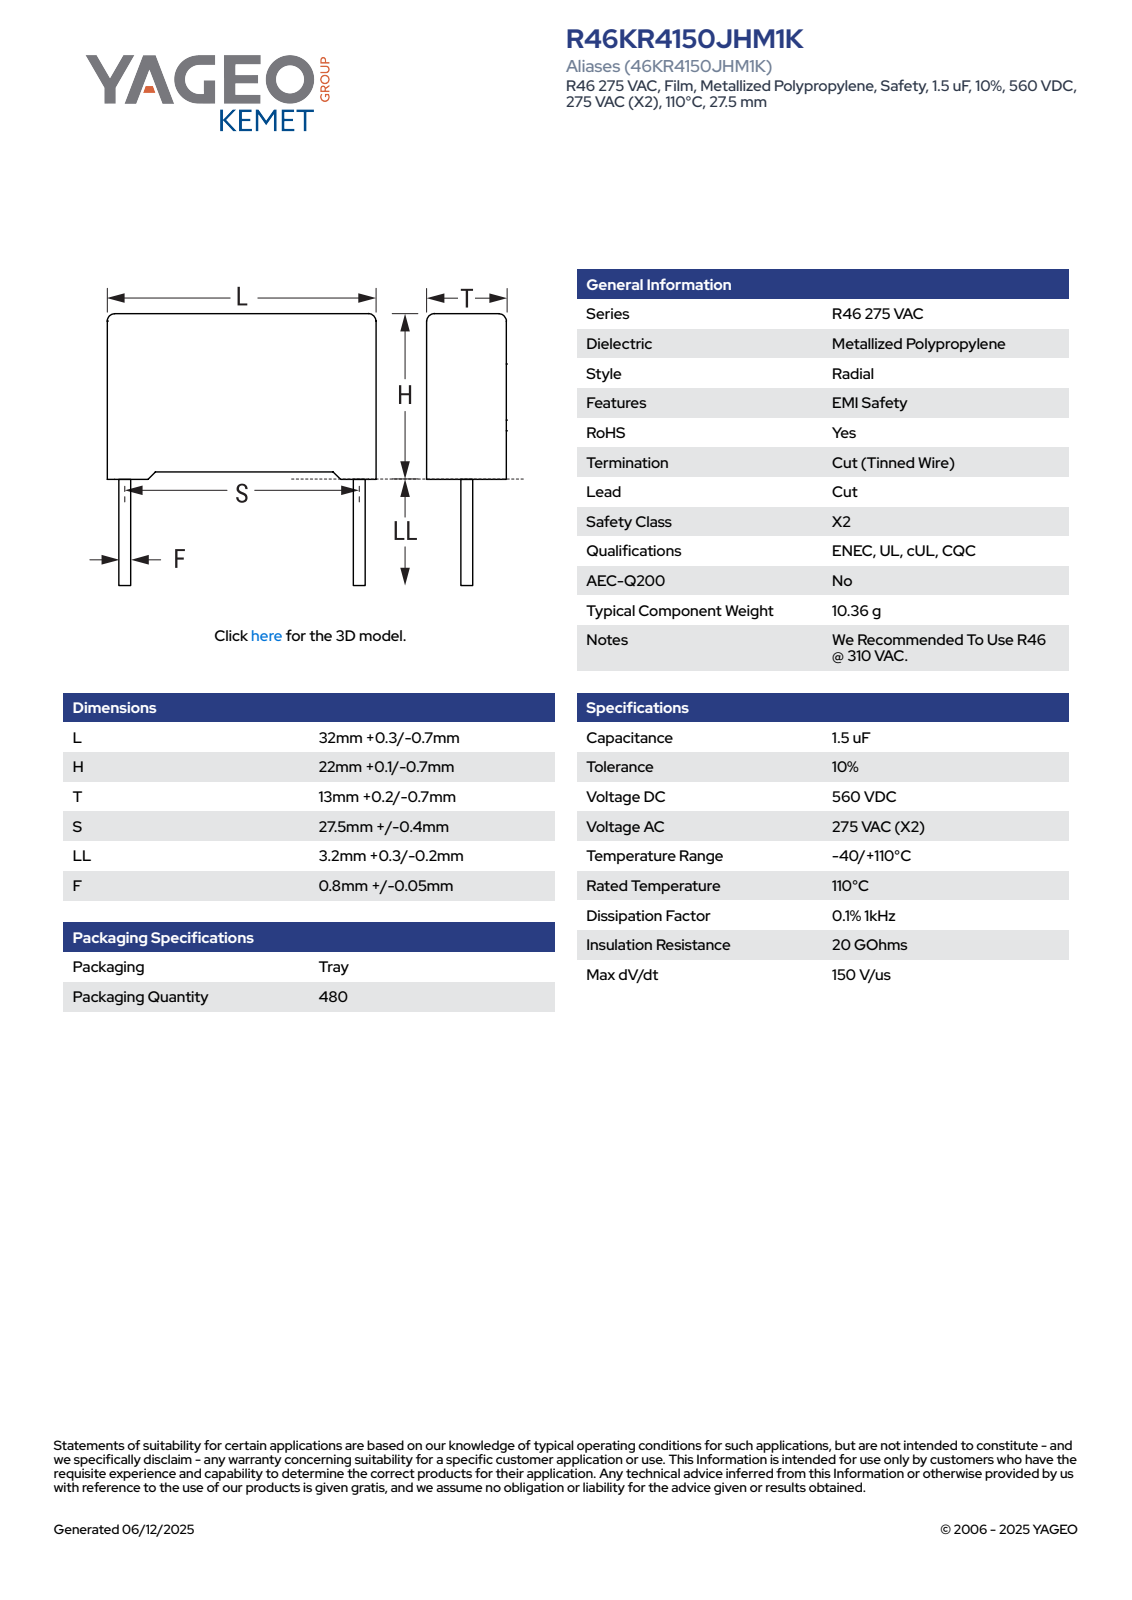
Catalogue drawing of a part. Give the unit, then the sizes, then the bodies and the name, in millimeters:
Units: millimetres
Overall size (bounding box): 32.3 × 25.6 × 13.21
Round bosses / shafts (diameter × count): ⌀0.85 ×2
Partial cylindrical surfaces — rounded edges, fillets, slot ends (radius × count): R0.5 ×4
Main face-to-face distances: 13.2, 21.34, 32.3, 21.35, 0.75, 0.76, 22.1, 1.08, 13.21, 31.22
Volume: 9 131 mm³ · Surface area: 2 937 mm²
Bodies: 4 solids, 85 faces (77 planar, 8 cylindrical, 0 other)
Part name (STEP PRODUCT): CFR_RB2_32X22X13_L32.3H22.1T13.2S27.5LL3.5F0.85
STEP written by: SolidWorks 2021 (AUTOMOTIVE_DESIGN)
